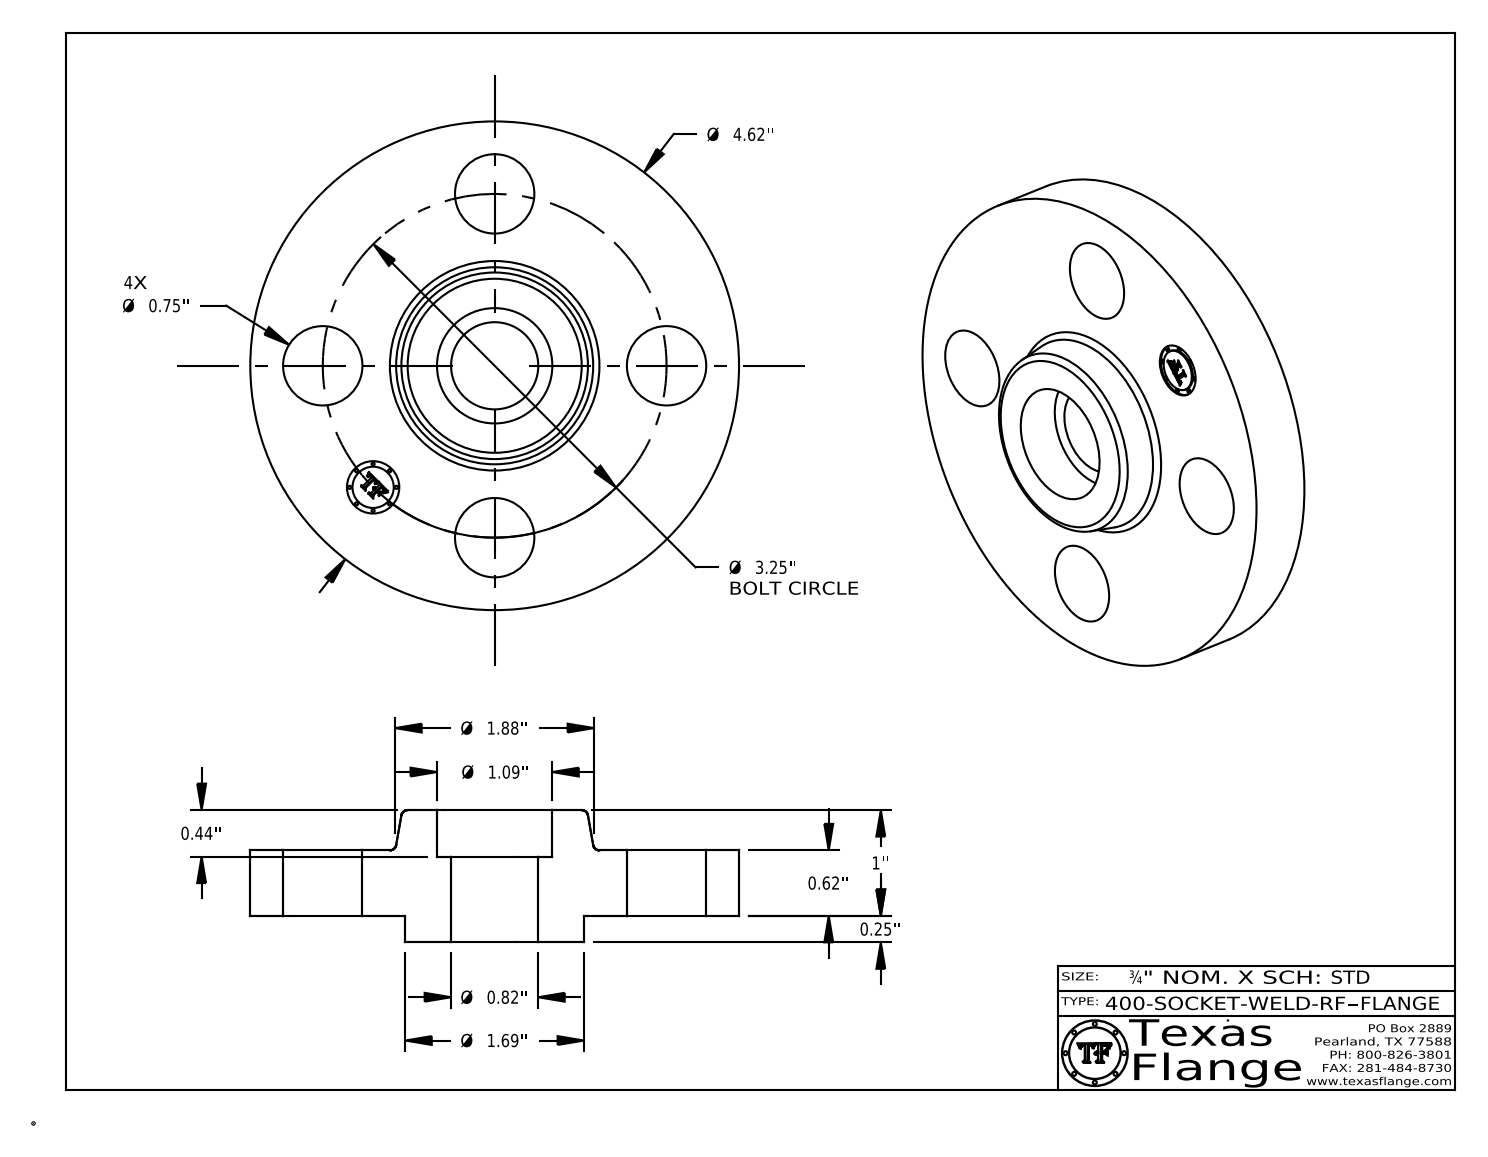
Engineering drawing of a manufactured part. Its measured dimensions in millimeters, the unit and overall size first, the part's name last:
Units: millimetres
Overall size (bounding box): 117.3 × 117.3 × 31.8
Round holes (diameter × count): ⌀19.1 ×4, ⌀12.6 ×1, ⌀20.9 ×1, ⌀27.7 ×1
Round bosses / shafts (diameter × count): ⌀0.8 ×8, ⌀117.3 ×1, ⌀42.9 ×1, ⌀9.9 ×1
Main face-to-face distances: 15.7, 6.4, 22.1, 31.8, 25.4, 9.7, 20.6, 14.2, 1.5, 11.2
Hole centre spacings: 41.3, 58.4, 31.6, 76.3, 82.6
Volume: 163 800 mm³ · Surface area: 32 530 mm²
Bodies: 1 solid, 412 faces (370 planar, 36 cylindrical, 6 other)
Part name (STEP PRODUCT): 400-SOCKET-WELD-RF
STEP written by: CATIA V5 STEP AP214 (AUTOMOTIVE_DESIGN)
